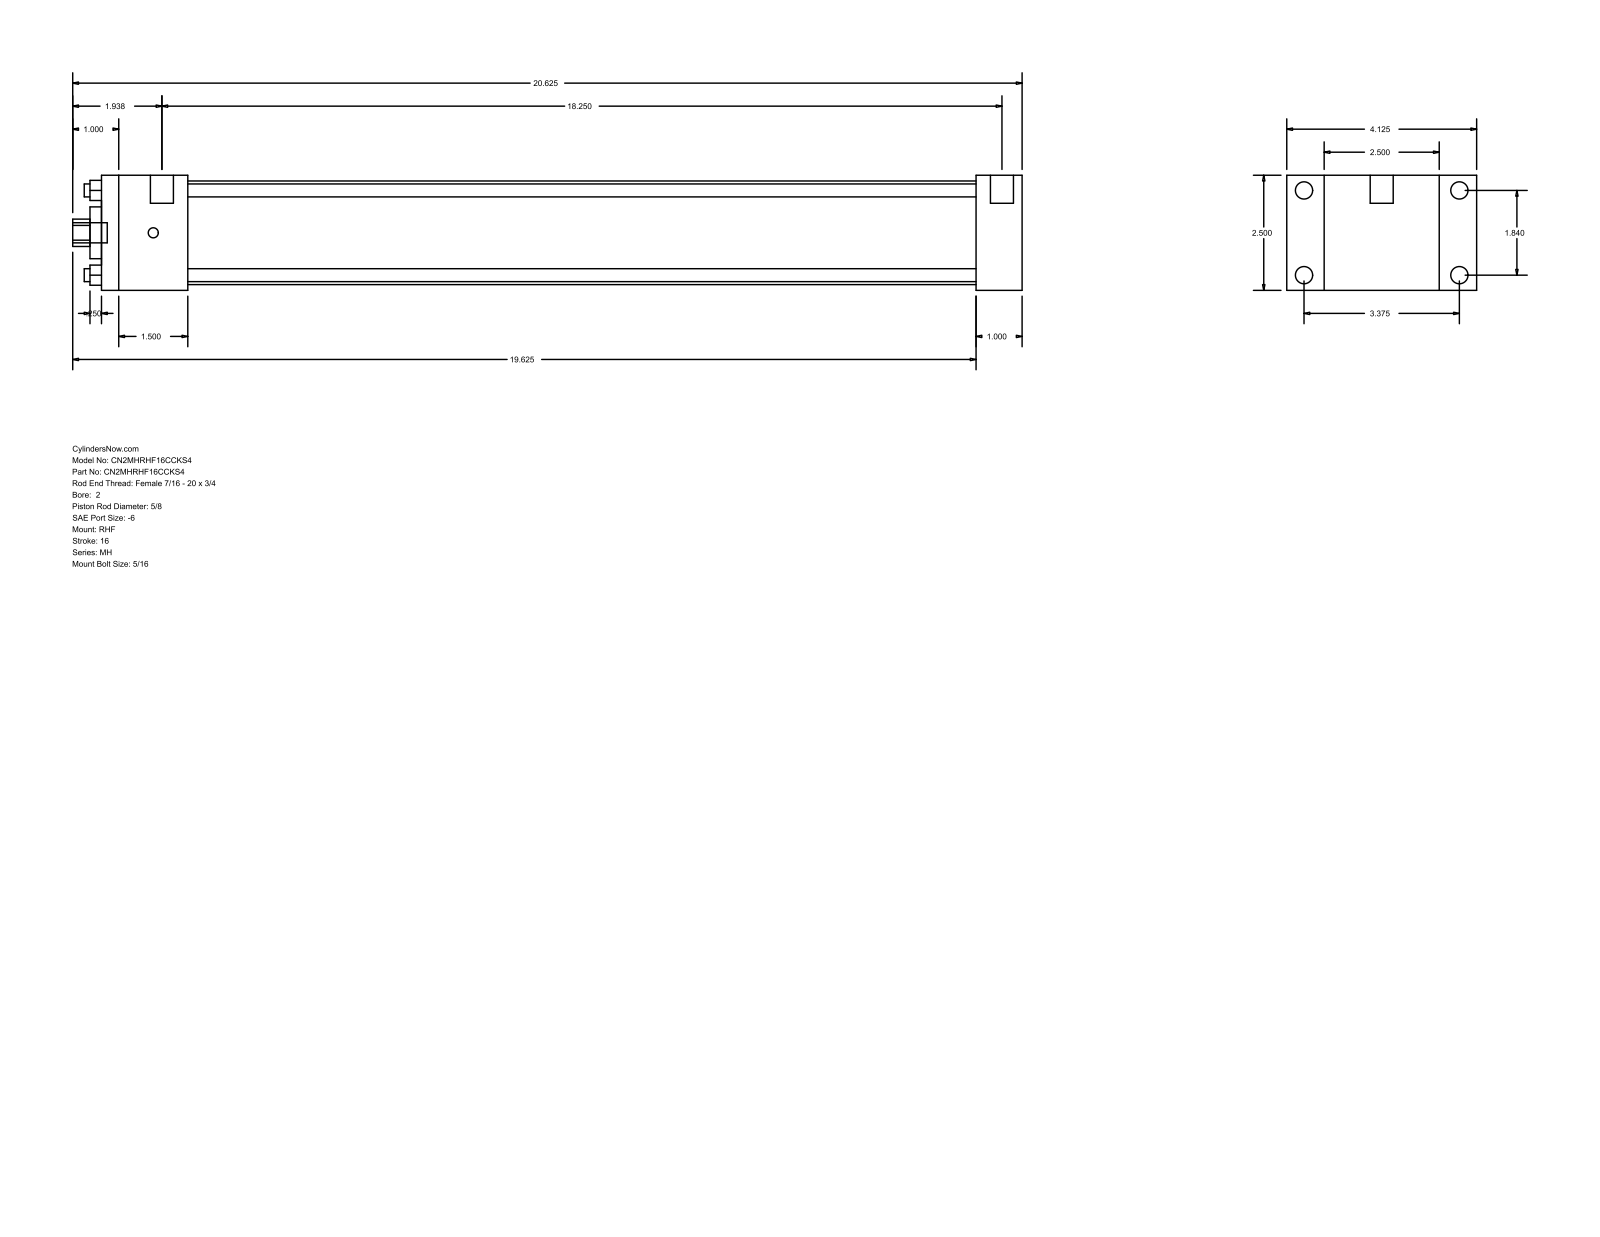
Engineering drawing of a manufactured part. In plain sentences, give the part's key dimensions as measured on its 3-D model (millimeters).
The part is named "MH_RHF__0200_0.625". Its 3-D file was written by "GSSL Pune (CONFIG_CONTROL_DESIGN)". It is 0 solids with 88 faces: 60 planar, 28 cylindrical and 0 other. Overall it measures 523.88 by 104.78 by 63.5 millimeters. Round holes: 4 of diameter 7.14, 1 of diameter 15.88, 1 of diameter 28.57, 1 of diameter 57.15. Round bosses or shafts: 4 of diameter 9.53, 4 of diameter 5.56, 2 of diameter 12.7, 1 of diameter 11.11. Partial cylindrical surfaces (rounded edges, fillets, slot ends): 1 of radius 7.54. The main face-to-face distances are 63.5, 25.4, 20.64, 84.14, 482.6, 508, 104.78, 47.62, 434.98, 460.38. The hole center spacings are 33.05, 46.74, 66.1.
